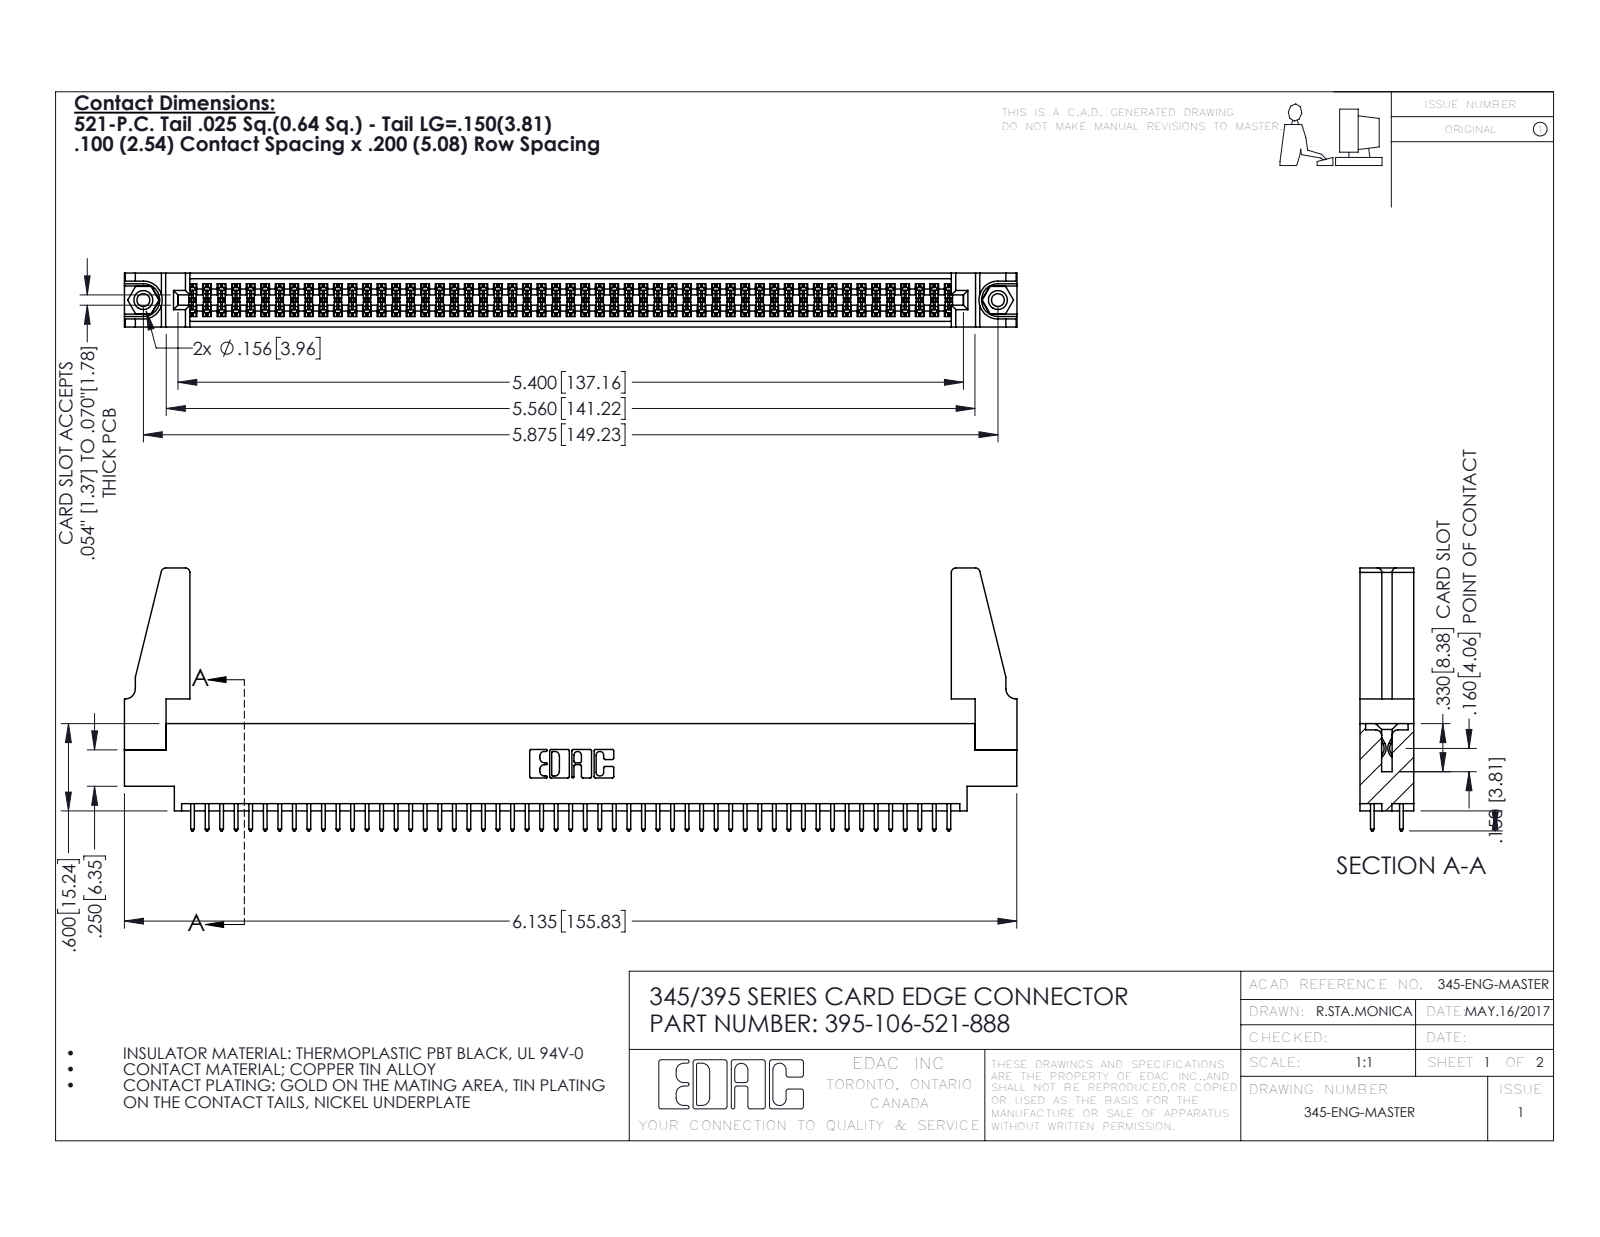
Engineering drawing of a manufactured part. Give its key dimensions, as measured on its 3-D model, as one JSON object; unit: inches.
{"part_name": "345-292-001_345-293-121; 345 Part_0.170 Offset - 0.156 Dia-TH; 395-106-521-888; 345-250-001_345-250-001-102 (+1 more)", "step_written_by": "SolidWorks 2016 (CONFIG_CONTROL_DESIGN)", "units": "inches", "bodies": {"solids": 111, "faces": 5554, "planar": 3654, "cylindrical": 1884, "other": 16}, "overall_size": [6.136, 1.807, 0.37], "volume_in3": 1.119, "surface_area_in2": 39.52, "round_holes": [[0.089, 2], [0.125, 2], [0.156, 2], [0.064, 1]], "round_bosses_or_shafts": [[0.155, 2]], "partial_cylinders_radius": [[0.006, 159], [0.01, 106], [0.01, 22], [0.03, 8], [0.007, 6], [0.031, 6], [0.026, 3], [0.014, 2]], "face_to_face_distances": [0.072, 0.298, 0.37, 0.2, 0.098, 0.272, 0.025, 0.225, 0.175, 0.149], "hole_center_spacings": [0.27, 5.639, 5.875]}
